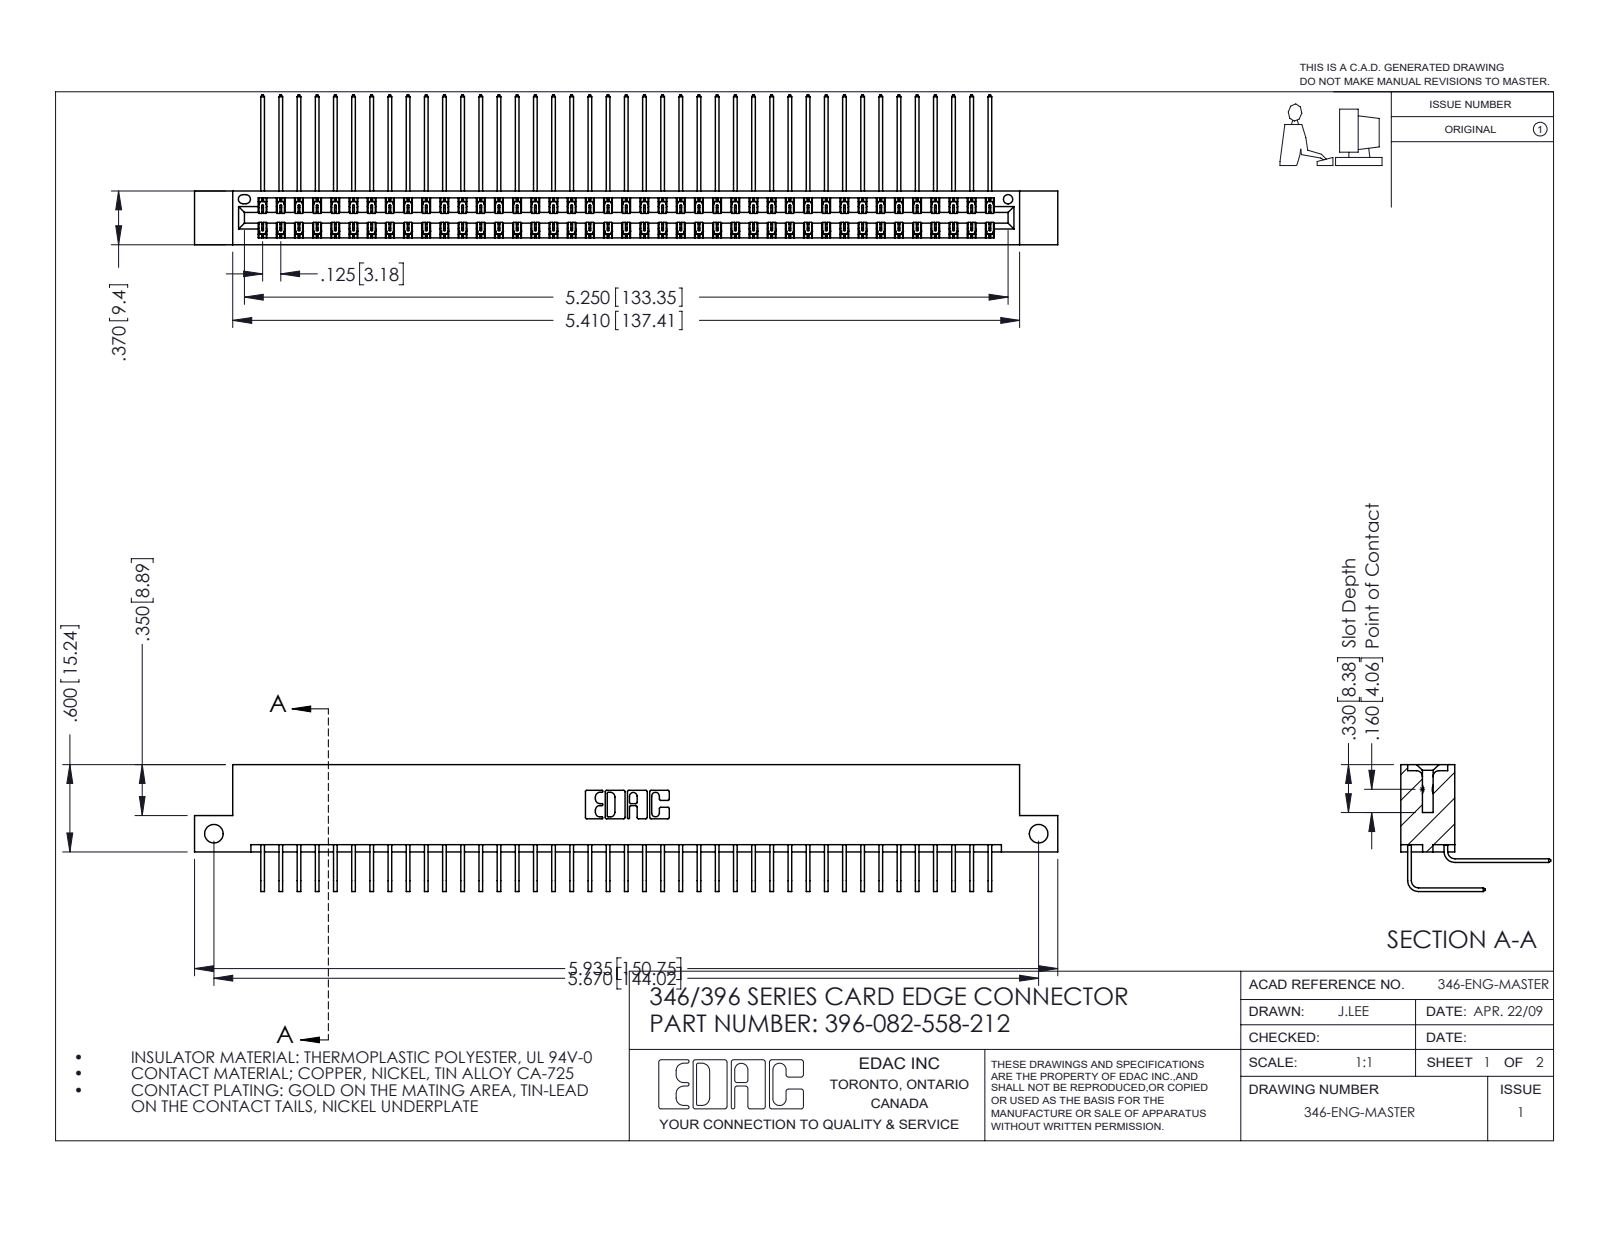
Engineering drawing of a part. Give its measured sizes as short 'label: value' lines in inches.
name: 345-292-001_558 Tail - 2; 345-292-001_558 559 Tail - 1; 396-082-558-212; 346 Part_Flush Mounting Lugs - Side Mount
written by: SolidWorks 2016 (CONFIG_CONTROL_DESIGN)
unit: in
bodies: 83 solids, 4550 faces (3110 planar, 1440 cylindrical, 0 other)
size: 5.935 × 1.03 × 0.873
volume: 0.92 in³; area: 35.4 in²
holes: 2× ⌀0.128, 1× ⌀0.064
rounds: 123× R0.006, 22× R0.01, 6× R0.007, 6× R0.031, 3× R0.026, 2× R0.014, 2× R0.022, 2× R0.024
face distances: 0.322, 0.048, 0.025, 0.37, 0.298, 0.25, 0.072, 0.275, 0.148, 0.222
hole spacings: 5.67
